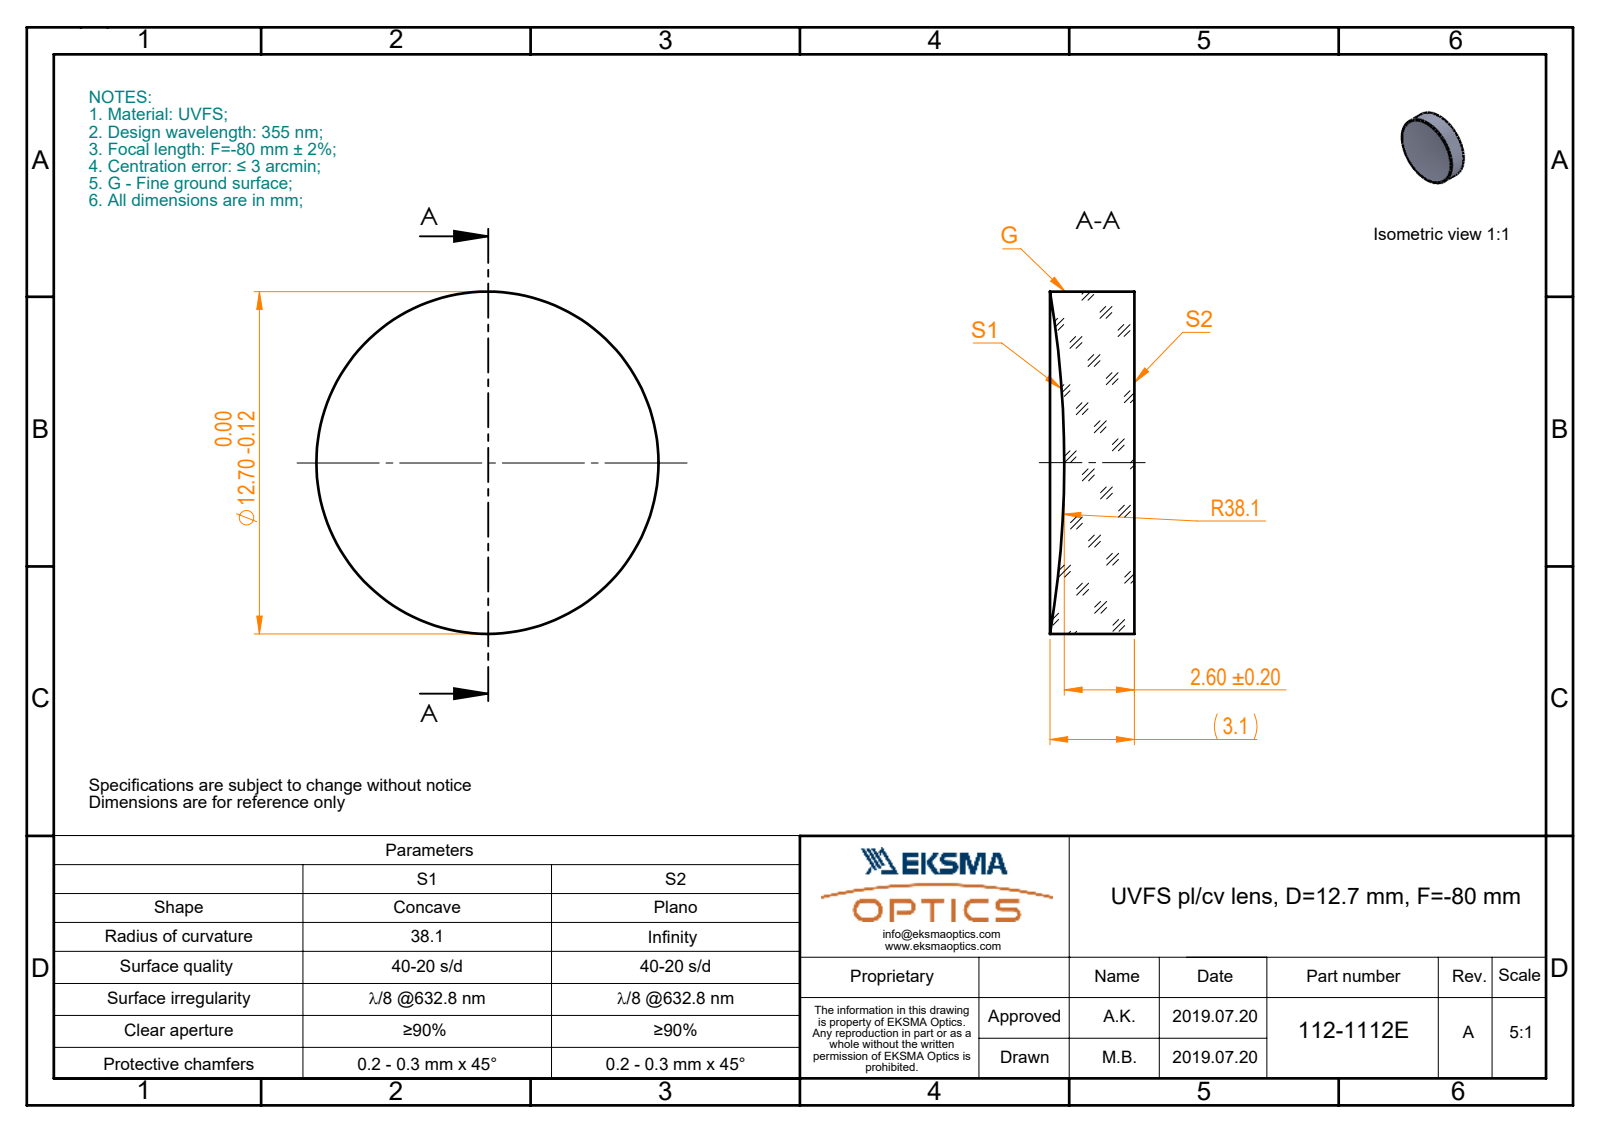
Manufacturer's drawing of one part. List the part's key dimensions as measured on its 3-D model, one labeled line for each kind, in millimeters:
Part name (STEP PRODUCT): 112-1112E UVFS pl-cv 12.7 F-80
STEP written by: SolidWorks 2017 (CONFIG_CONTROL_DESIGN)
Units: millimetres
Bodies: 1 solid, 5 faces (1 planar, 2 cylindrical, 2 other)
Overall size (bounding box): 12.7 × 12.7 × 3.13
Volume: 363 mm³ · Surface area: 379 mm²
Round bosses / shafts (diameter × count): ⌀12.7 ×1
